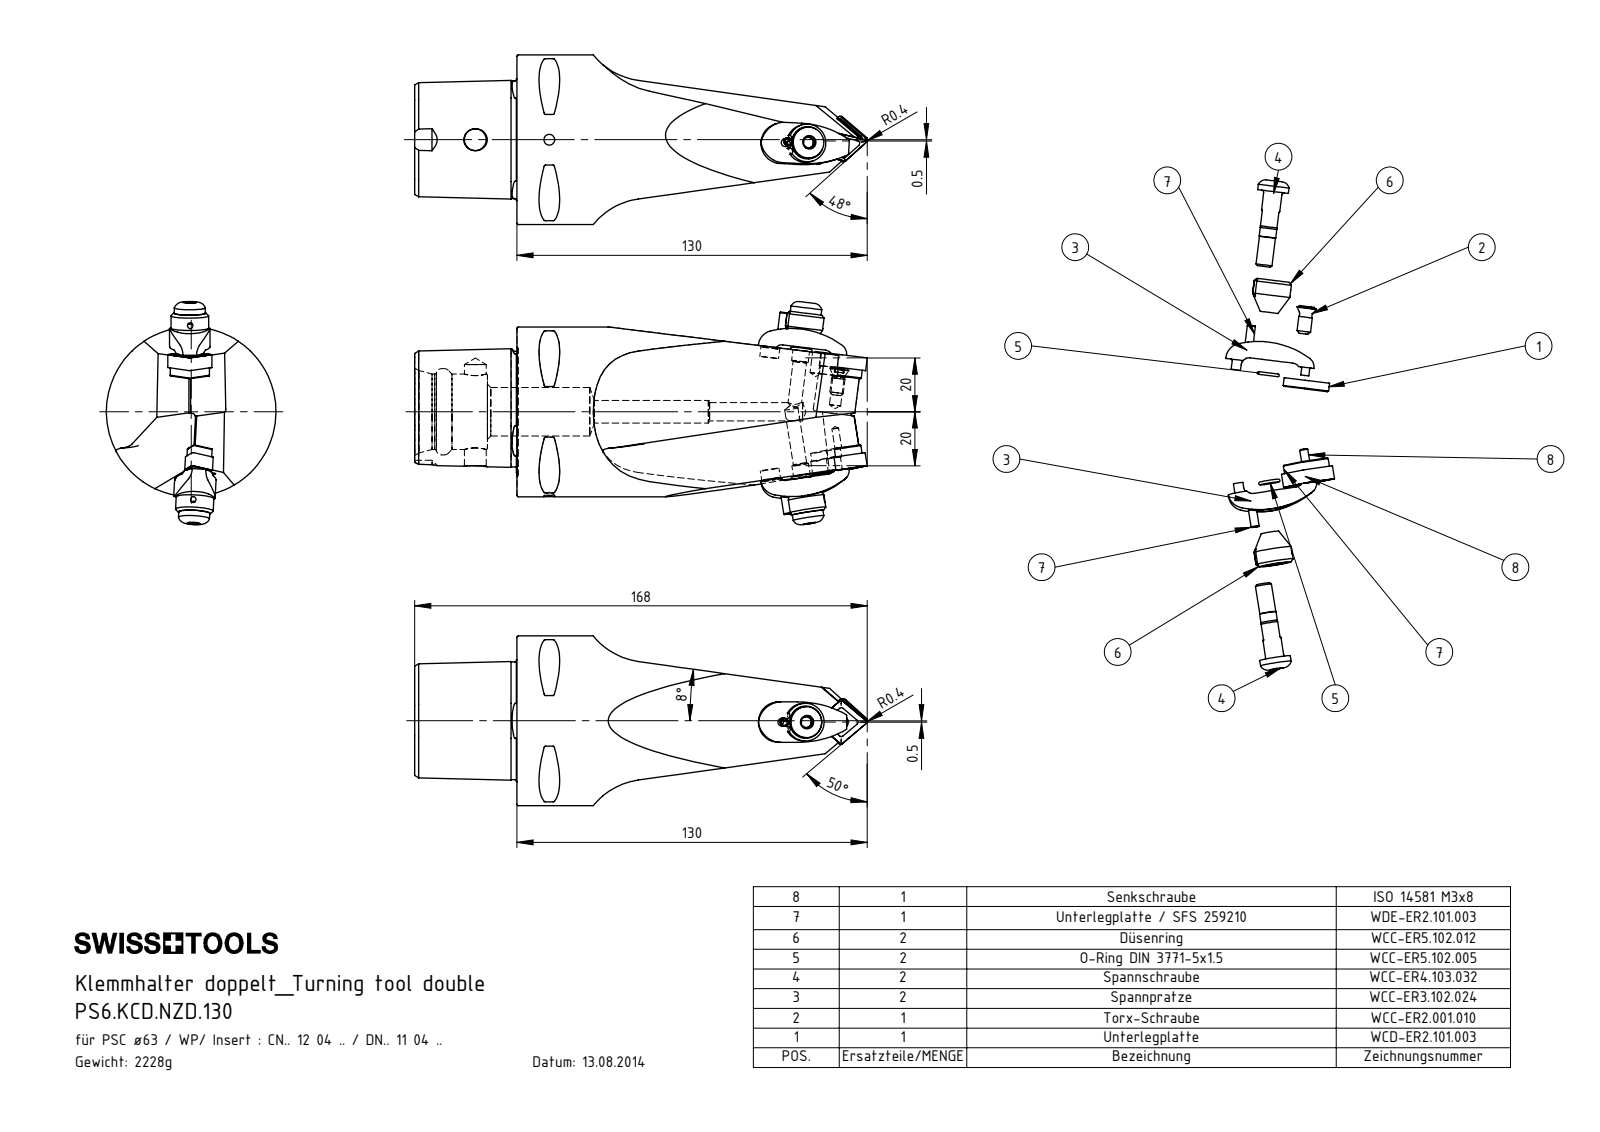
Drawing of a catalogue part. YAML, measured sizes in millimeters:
part_name: "PS6-KCD.NZD.130; ISO 14581 - M3x8; WDE-ER2.101.003_A; DNMG110404 (+8 more)"
step_written_by: "SolidWorks 2012 (CONFIG_CONTROL_DESIGN)"
units: millimeters
bodies: {solids: 17, faces: 662, planar: 176, cylindrical: 220, other: 266}
overall_size: [168, 82.74, 63]
volume: 283386
surface_area: 48097
round_holes:
  - {diameter: 2, count: 6}
  - {diameter: 7, count: 4}
  - {diameter: 2.4, count: 2}
  - {diameter: 3, count: 2}
  - {diameter: 4.2, count: 2}
  - {diameter: 5, count: 2}
  - {diameter: 6.2, count: 2}
  - {diameter: 8.5, count: 2}
  - {diameter: 2.5, count: 1}
  - {diameter: 3.81, count: 1}
  - {diameter: 4, count: 1}
  - {diameter: 4.8, count: 1}
round_bosses_or_shafts:
  - {diameter: 3, count: 5}
  - {diameter: 14, count: 2}
  - {diameter: 11.5, count: 2}
  - {diameter: 6.8, count: 2}
  - {diameter: 6.2, count: 2}
  - {diameter: 6, count: 2}
  - {diameter: 4, count: 2}
  - {diameter: 63, count: 1}
partial_cylinders:
  - {radius: 0.4, count: 12}
  - {radius: 0.5, count: 8}
  - {radius: 0.31, count: 6}
  - {radius: 0.35, count: 6}
  - {radius: 0.39, count: 6}
  - {radius: 0.69, count: 6}
  - {radius: 1.5, count: 6}
  - {radius: 1, count: 4}
face_to_face_distances: [19.64, 38, 11, 24.88, 1.3, 12.7, 27, 4.46, 3.18, 5.76]
hole_center_spacings: [8, 8.2, 22.32, 6.37, 14.11, 14.29, 14.33, 14.37]
